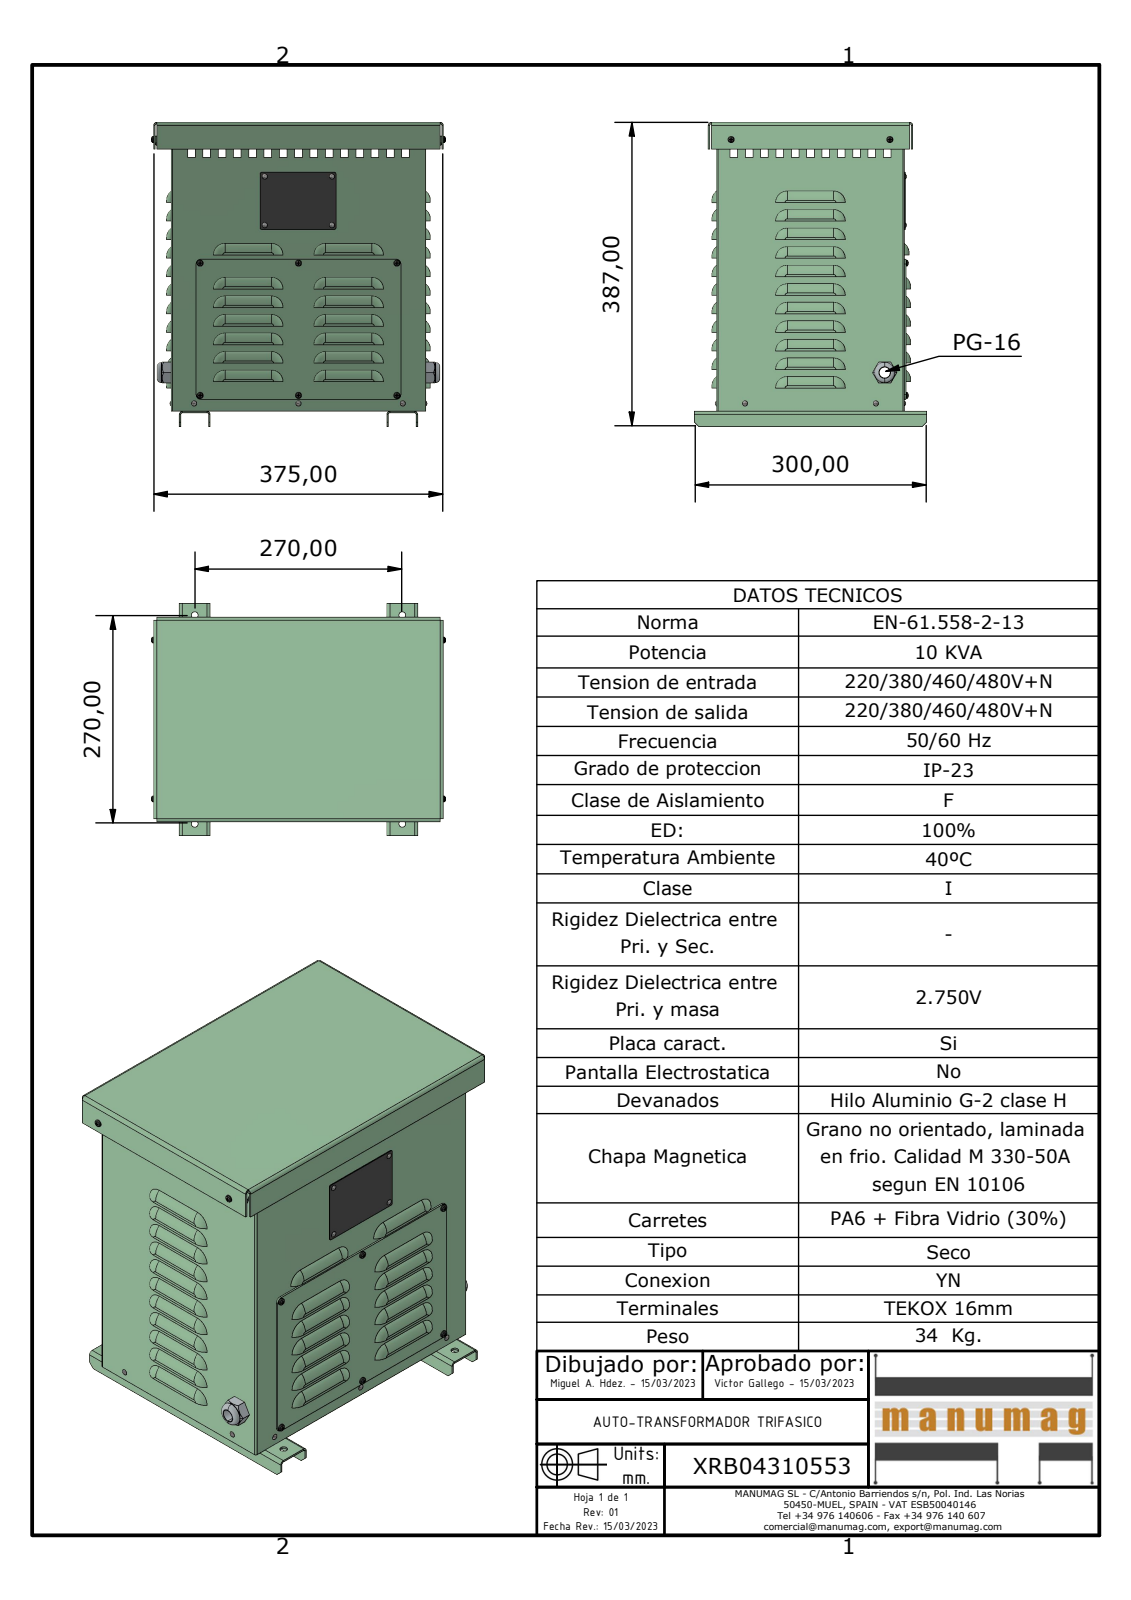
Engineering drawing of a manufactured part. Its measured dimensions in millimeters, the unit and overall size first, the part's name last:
Units: millimetres
Overall size (bounding box): 394.02 × 381.14 × 300
Round holes (diameter × count): ⌀2.3 ×8, ⌀3.7 ×8, ⌀8.8 ×8, ⌀4.3 ×5, ⌀3.4 ×4, ⌀4 ×4, ⌀5 ×3, ⌀14 ×1, ⌀24 ×1
Round bosses / shafts (diameter × count): ⌀3.2 ×9, ⌀4 ×8, ⌀3.62 ×8, ⌀26 ×1, ⌀23 ×1, ⌀22.5 ×1
Partial cylindrical surfaces — rounded edges, fillets, slot ends (radius × count): R14 ×105, R4 ×68, R15 ×40, R2 ×20, R1.5 ×6, R2 ×5, R6 ×4
Main face-to-face distances: 2, 240.62, 327.32, 372.01, 242.62, 374.01, 238.62, 325.32, 329.32, 4
Hole centre spacings: 55.99, 127.3, 168.89, 210.03, 213.21, 213.3, 342.86, 62.98
Volume: 1 720 000 mm³ · Surface area: 1 517 000 mm²
Bodies: 33 solids, 1975 faces (1082 planar, 421 cylindrical, 472 other)
Part name (STEP PRODUCT): XRB04310553; JE010 EXPORT BASE; JE010 EXPORT PATA; JE010 EXPORT CUERPO (+6 more)
STEP written by: Autodesk Inventor 2023 (AUTOMOTIVE_DESIGN)
